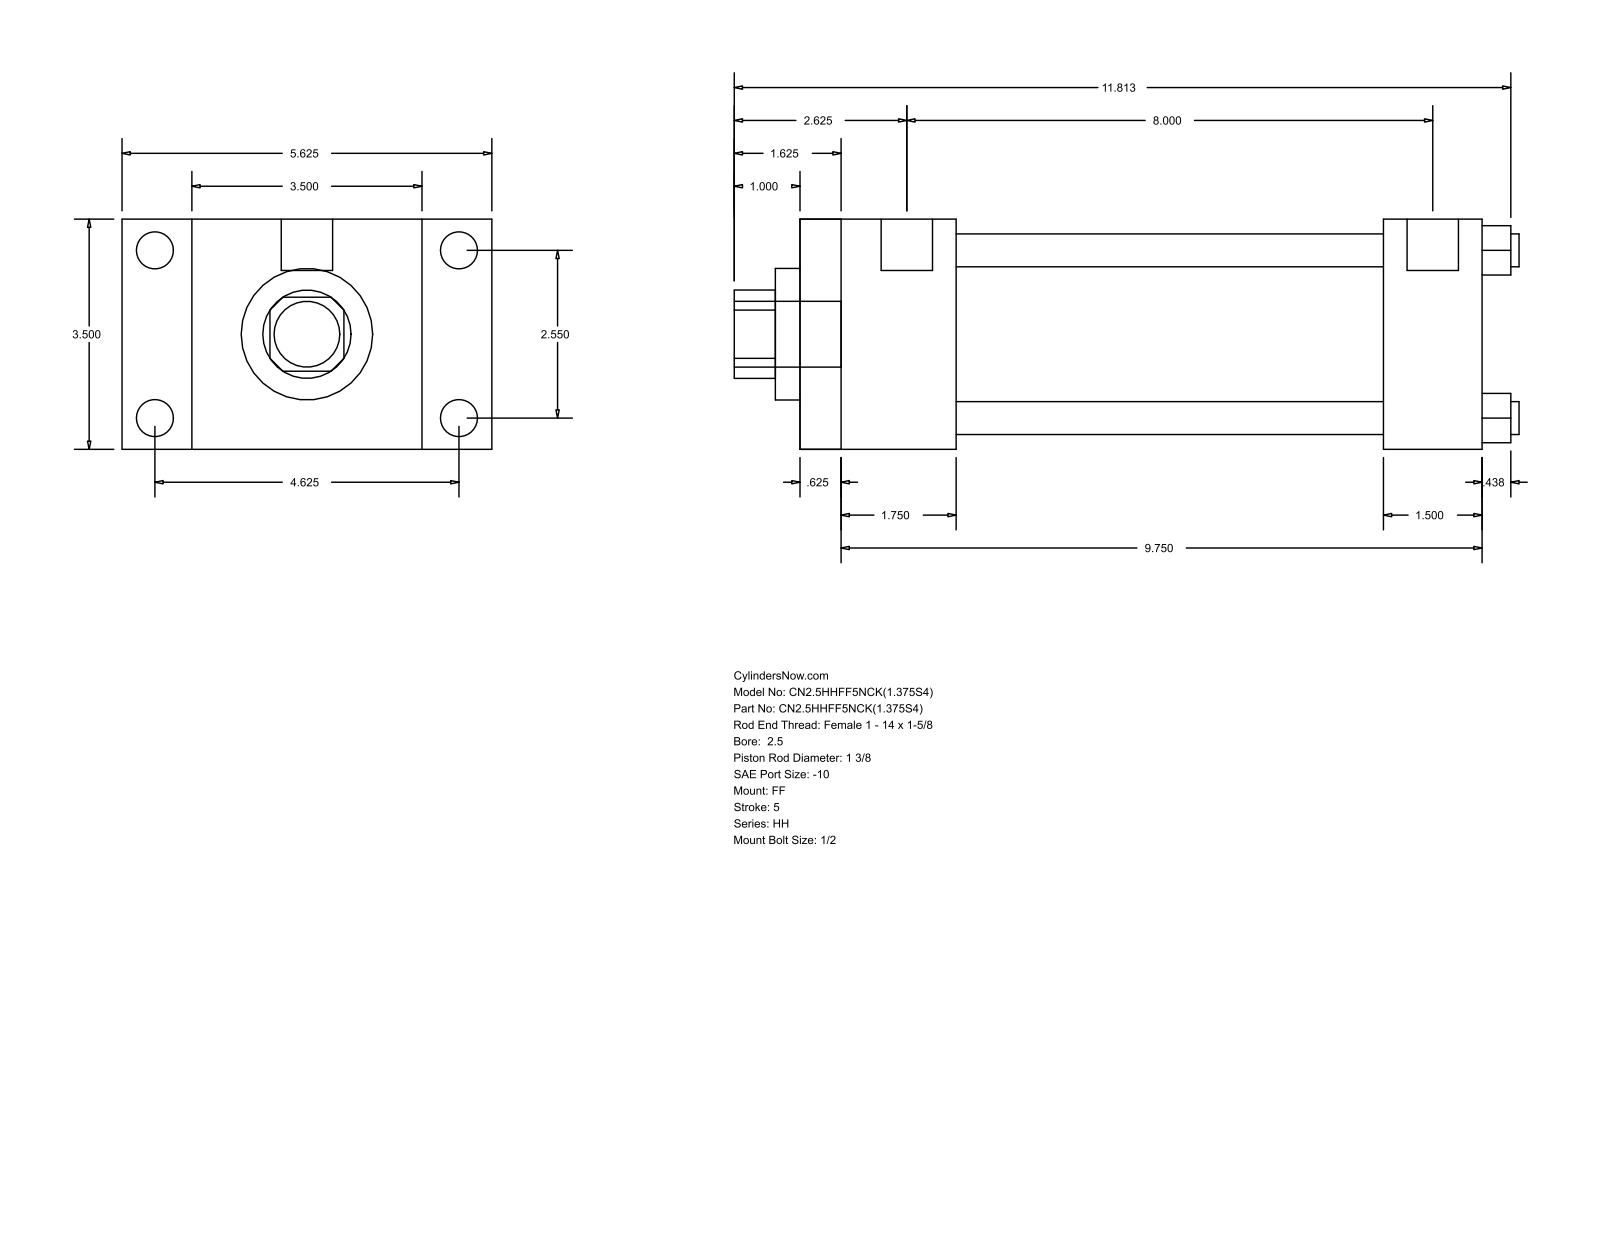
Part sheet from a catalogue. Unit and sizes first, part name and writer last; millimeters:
Units: millimetres
Overall size (bounding box): 303.21 × 142.88 × 88.9
Round holes (diameter × count): ⌀12.7 ×4, ⌀34.92 ×1, ⌀50.8 ×1, ⌀73.03 ×1
Round bosses / shafts (diameter × count): ⌀14.3 ×4, ⌀5.56 ×4, ⌀19.84 ×2, ⌀25.4 ×1
Partial cylindrical surfaces — rounded edges, fillets, slot ends (radius × count): R17.06 ×1
Main face-to-face distances: 88.9, 263.53, 15.87, 247.66, 60.32, 44.45, 203.21, 225.42, 209.55, 165.1
Hole centre spacings: 45.79, 64.76, 91.58
Bodies: 0 solids, 92 faces (64 planar, 28 cylindrical, 0 other)
Part name (STEP PRODUCT): HH_FF__0250_1.375
STEP written by: GSSL Pune (CONFIG_CONTROL_DESIGN)
